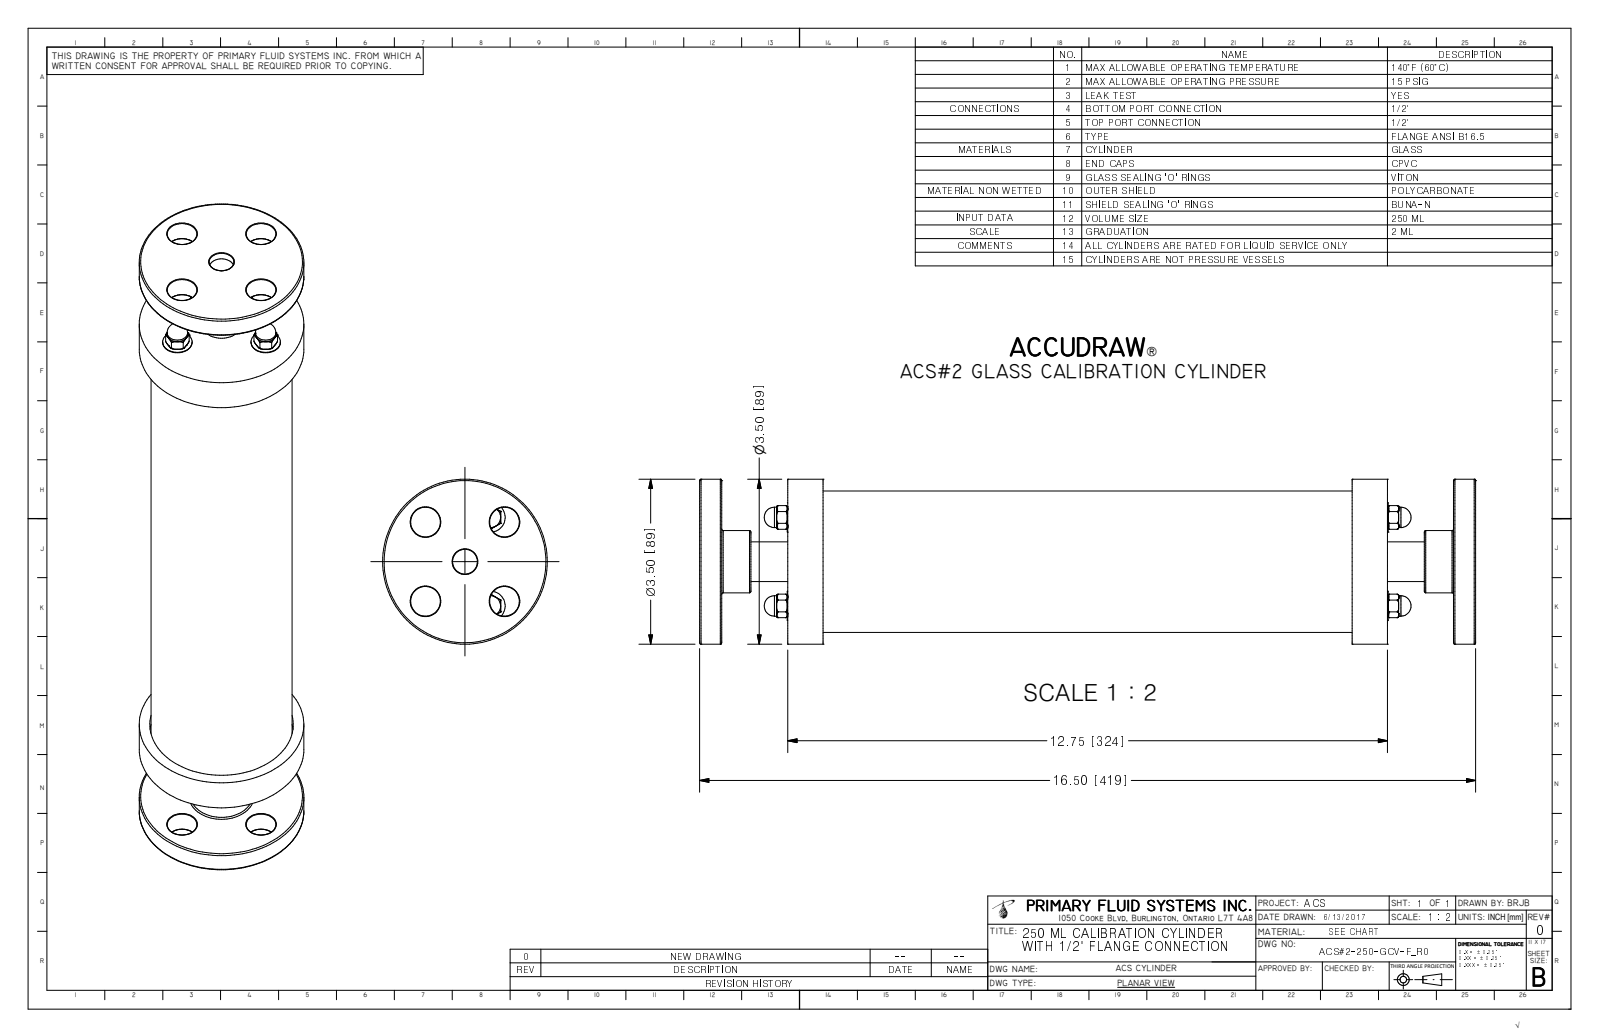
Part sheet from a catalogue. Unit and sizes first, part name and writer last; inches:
Units: inches
Overall size (bounding box): 16.5 × 3.5 × 3.5
Round holes (diameter × count): ⌀0.63 ×4, ⌀0.18 ×3, ⌀0.201 ×3, ⌀0.281 ×3, ⌀0.526 ×1, ⌀2.75 ×1, ⌀3.05 ×1
Round bosses / shafts (diameter × count): ⌀0.625 ×3, ⌀0.187 ×3, ⌀3.5 ×1, ⌀3 ×1, ⌀2.7 ×1, ⌀1.575 ×1, ⌀1.32 ×1
Main face-to-face distances: 1.405, 14.155, 12, 2.155, 13.405, 0.75, 12.75, 1.875, 14.625, 16.5
Hole centre spacings: 1.188, 1.68, 1.084, 0.314, 0.874, 1.385, 1.803, 1.878
Volume: 59.27 in³ · Surface area: 429.9 in²
Bodies: 1 solid, 494 faces (41 planar, 77 cylindrical, 376 other)
Part name (STEP PRODUCT): ACS#2-250-GCV-F_R0
STEP written by: Autodesk Inventor 2009 (AUTOMOTIVE_DESIGN)
